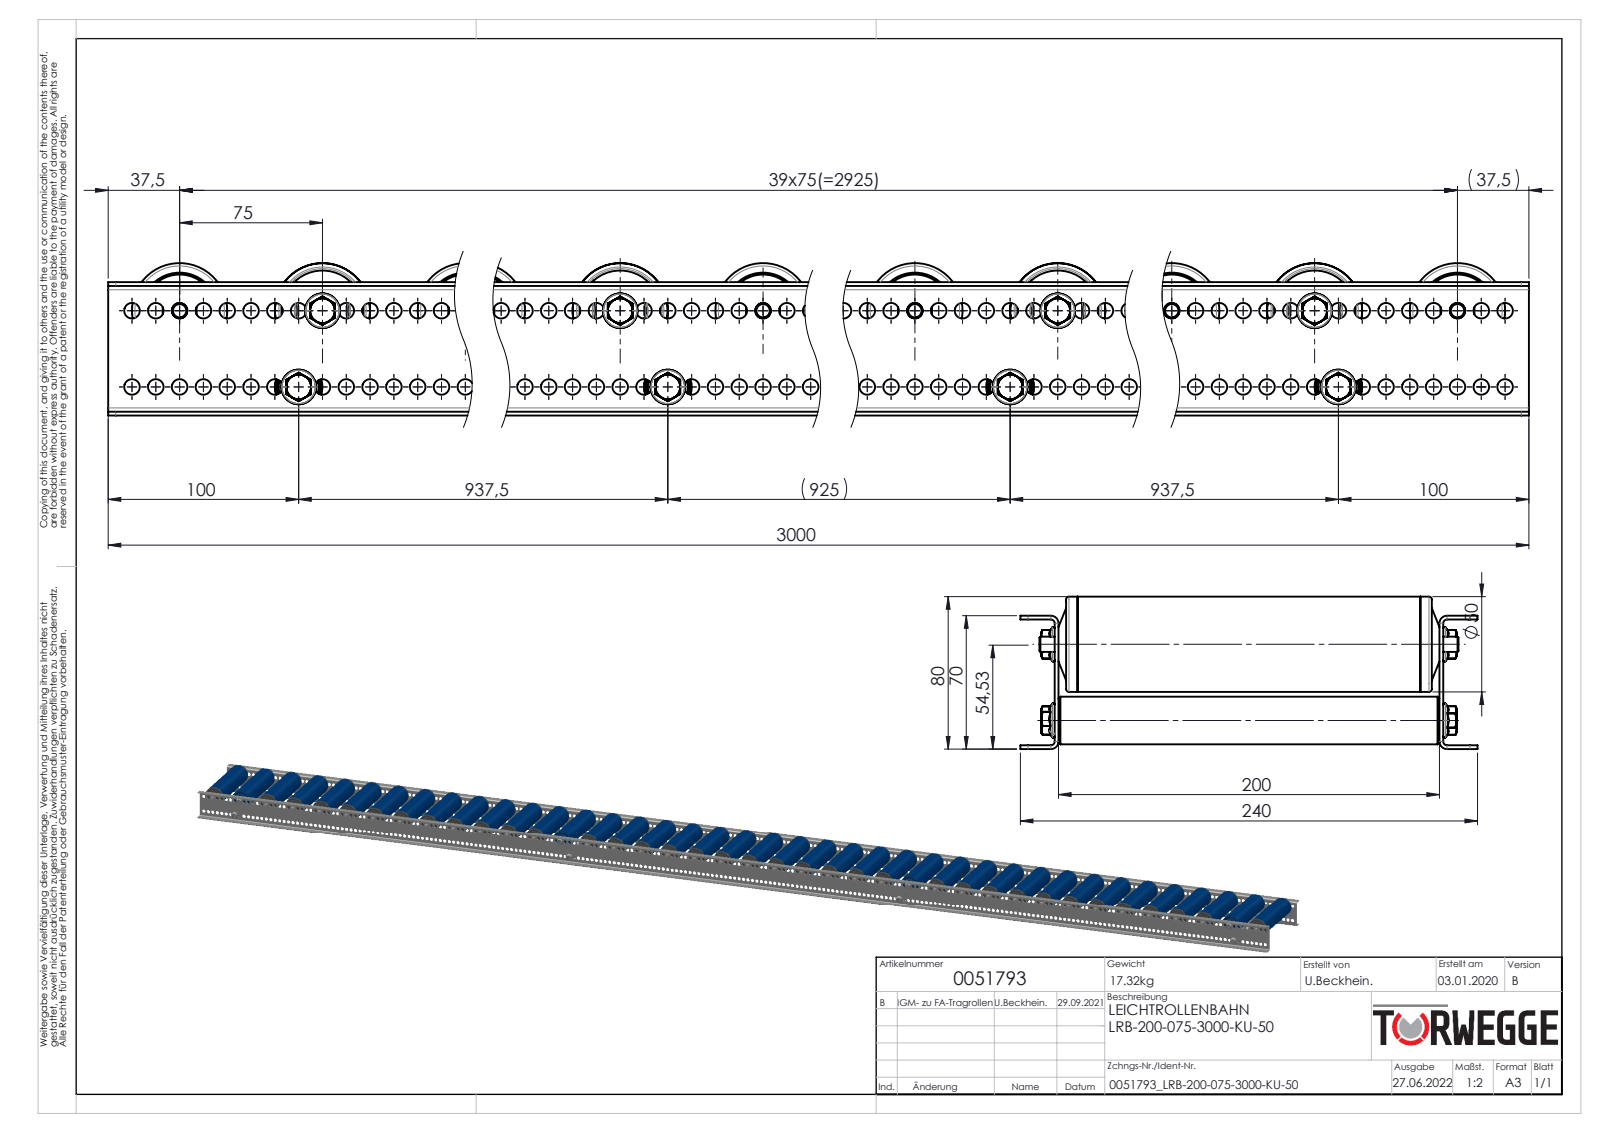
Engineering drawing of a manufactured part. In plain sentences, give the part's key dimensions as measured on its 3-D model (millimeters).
The part is named "0026267_Typ-KUT100-50x2,8-8_Lageboden-schematisch; 0017015_Tragrollenrohr-Ø50x2,8KU_KFG_0017015_L=185; KUT100-50x2,8-KB-A8-FA_KFG_0034512_KUT100-50x2,8-KB-A8-FA-EL=200; 0024178_Passscheibe_DIN988_12x18x1 (+8 more)". Its 3-D file was written by "SolidWorks 2020 (AUTOMOTIVE_DESIGN)". It is 634 solids with 12132 faces: 2988 planar, 5696 cylindrical and 3448 other. Overall it measures 3000 by 240 by 80 millimeters. Its volume is 6 966 000 cubic millimeters and its surface area 5 418 000 square millimeters. Round holes: 478 of diameter 8.2, 36 of diameter 7.6, 36 of diameter 8, 36 of diameter 25, 36 of diameter 30, 36 of diameter 35, 36 of diameter 39.4, 36 of diameter 40, 8 of diameter 6.8, 4 of diameter 12, 4 of diameter 12.1, 4 of diameter 16. Round bosses or shafts: 40 of diameter 50, 36 of diameter 44.4, 36 of diameter 38, 36 of diameter 36, 36 of diameter 33, 36 of diameter 22, 36 of diameter 21, 8 of diameter 25. Partial cylindrical surfaces (rounded edges, fillets, slot ends): 72 of radius 0.6, 72 of radius 0.75, 72 of radius 2.45, 36 of radius 4.87, 36 of radius 7, 8 of radius 4, 4 of radius 2. The main face-to-face distances are 2, 202, 68, 200, 204, 70, 66, 192, 12, 6. The hole center spacings are 12.5, 25, 37.5, 50, 62.5, 75, 87.5, 100.
